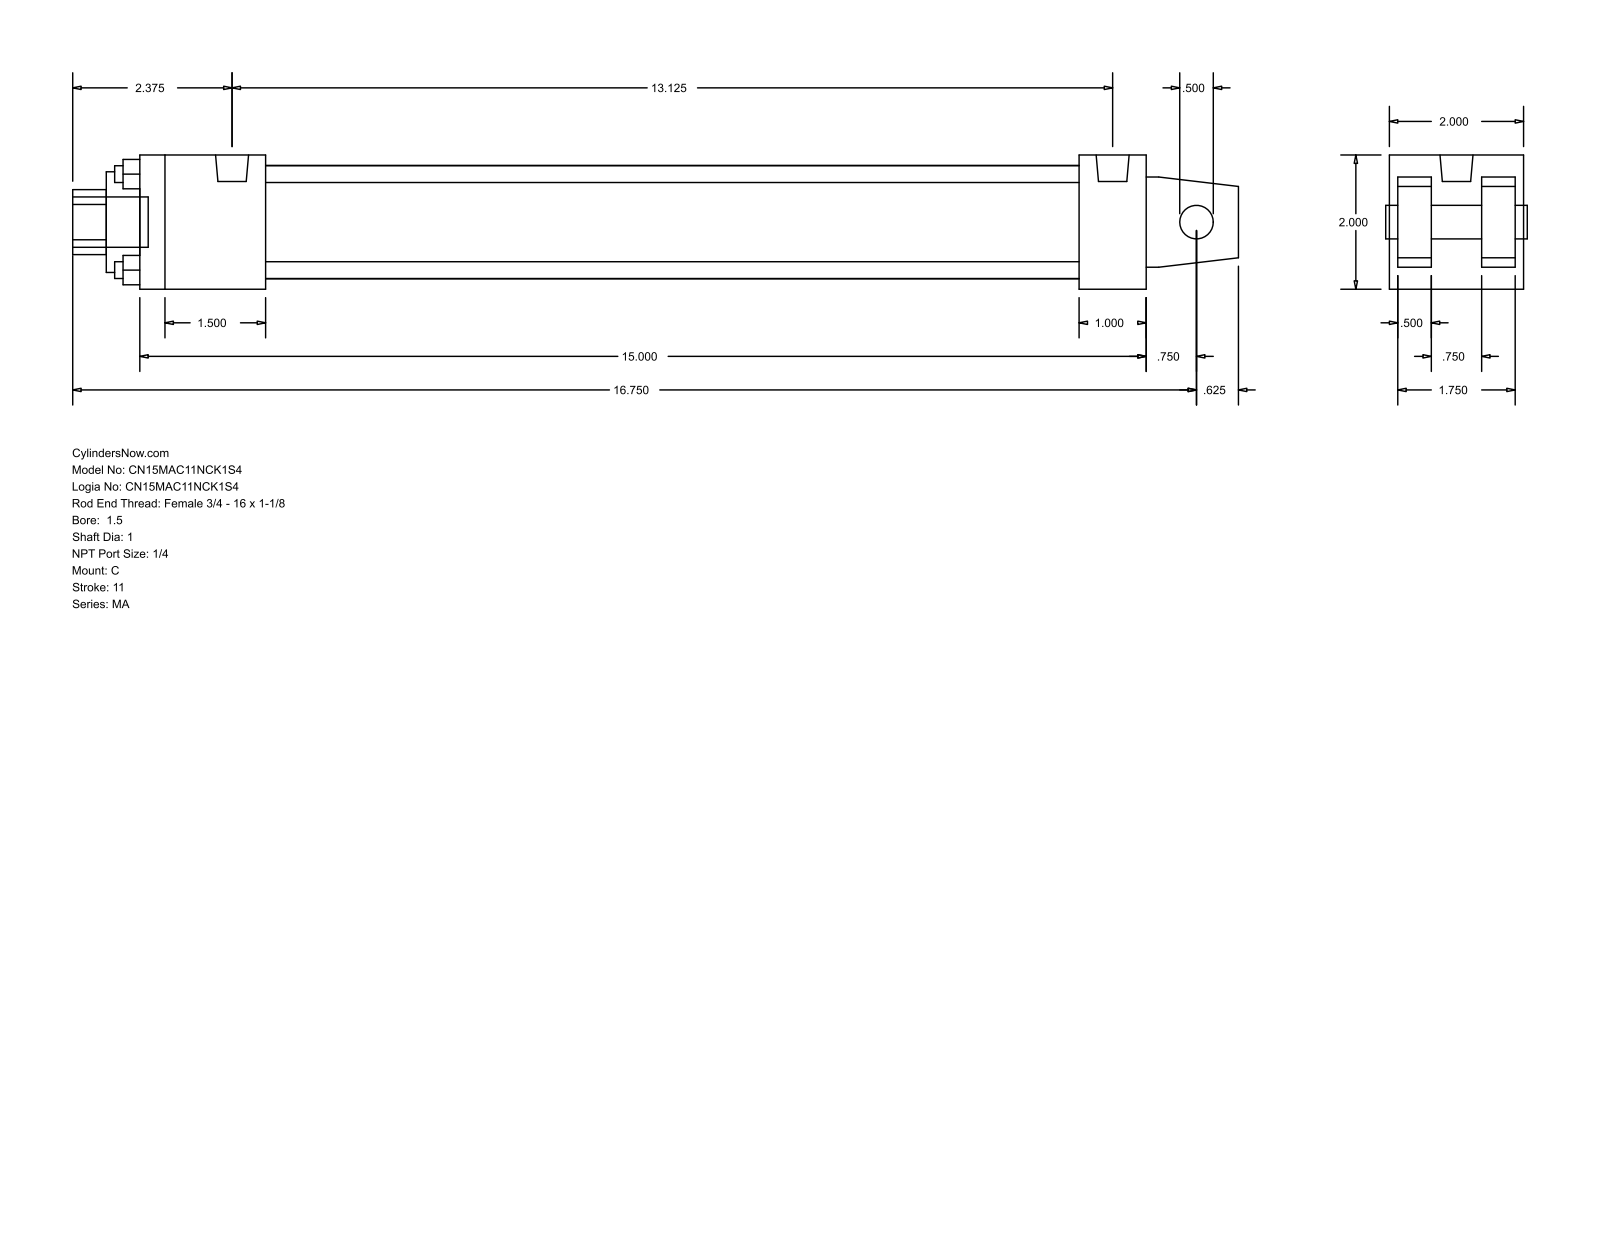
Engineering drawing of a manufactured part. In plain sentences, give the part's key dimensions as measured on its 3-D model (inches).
The part is named "MA_C__0150_1". Its 3-D file was written by "GSSL Pune (CONFIG_CONTROL_DESIGN)". It is 0 solids with 103 faces: 76 planar, 27 cylindrical and 0 other. Overall it measures 17.375 by 2 by 2 inches. Round holes: 4 of diameter 0.25, 1 of diameter 0.5, 1 of diameter 1, 1 of diameter 1.5, 1 of diameter 1.69. Round bosses or shafts: 4 of diameter 0.313, 2 of diameter 0.492, 1 of diameter 0.75. Partial cylindrical surfaces (rounded edges, fillets, slot ends): 1 of radius 0.484. The main face-to-face distances are 2, 1.875, 0.5, 0.125, 0.625, 1.375, 1.25, 1.75, 15, 1. The hole center spacings are 1.011, 1.43, 2.022.
